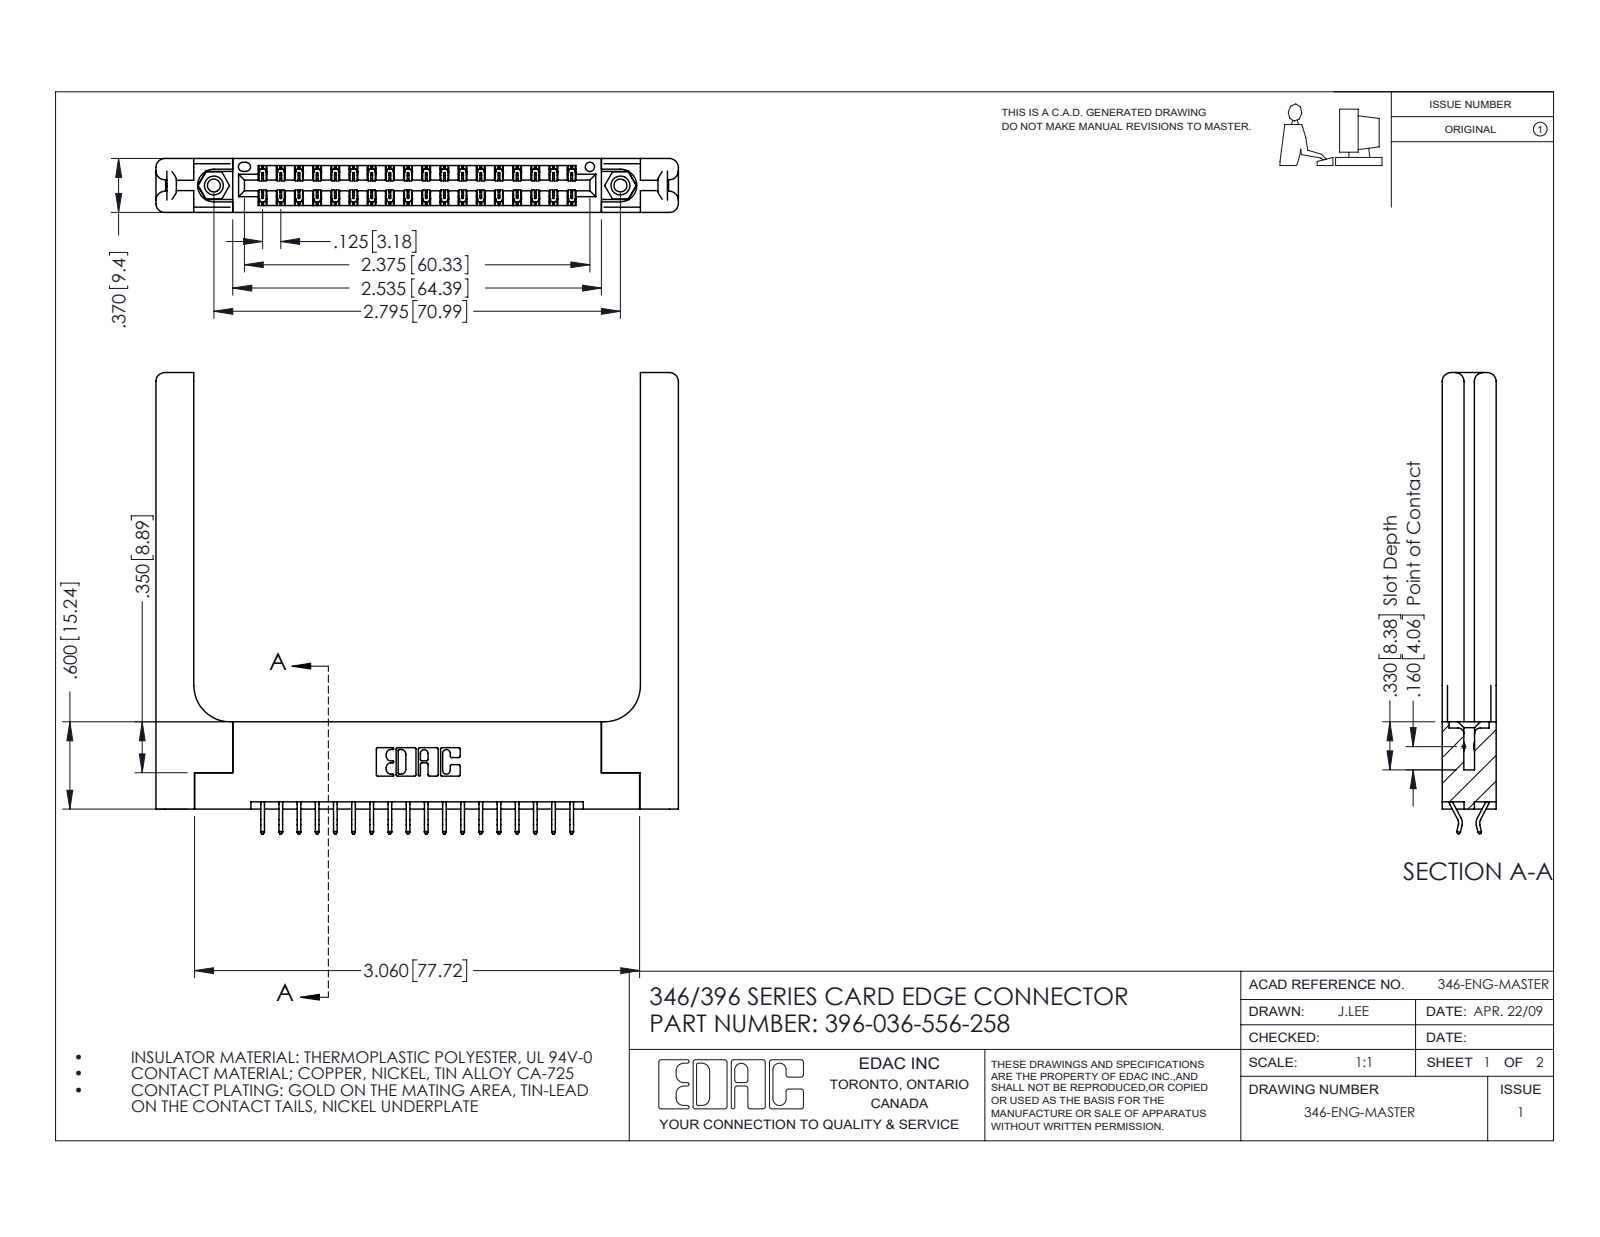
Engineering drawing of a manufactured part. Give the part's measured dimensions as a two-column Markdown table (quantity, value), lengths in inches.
| quantity | value |
| --- | --- |
| part name | 345-292-001_556 Tail; 346-220-058_345-220-058; 346 Part_Flush Mounting Lugs - 0.156 Dia-TH; 396-036-556-258 (+1 more) |
| STEP written by | SolidWorks 2016 (CONFIG_CONTROL_DESIGN) |
| units | inches |
| bodies | 41 solids, 2466 faces (1628 planar, 778 cylindrical, 60 other) |
| overall size | 3.591 × 3.17 × 0.37 |
| volume | 0.989 in³ |
| surface area | 25.62 in² |
| round holes (diameter × count) | 0.089 × 2, 0.125 × 2, 0.156 × 2, 0.064 × 1 |
| round bosses / shafts (diameter × count) | 0.155 × 2 |
| partial cylindrical surfaces (radius × count) | 0.006 × 54, 0.01 × 22, 0.06 × 16, 0.007 × 6, 0.031 × 6, 0.026 × 3, 0.01 × 2, 0.014 × 2 |
| main face-to-face distances | 0.37, 0.15, 0.072, 0.148, 0.048, 0.322, 0.25, 0.102, 0.22, 0.173 |
| hole center spacings | 0.246, 2.588, 2.795 |
